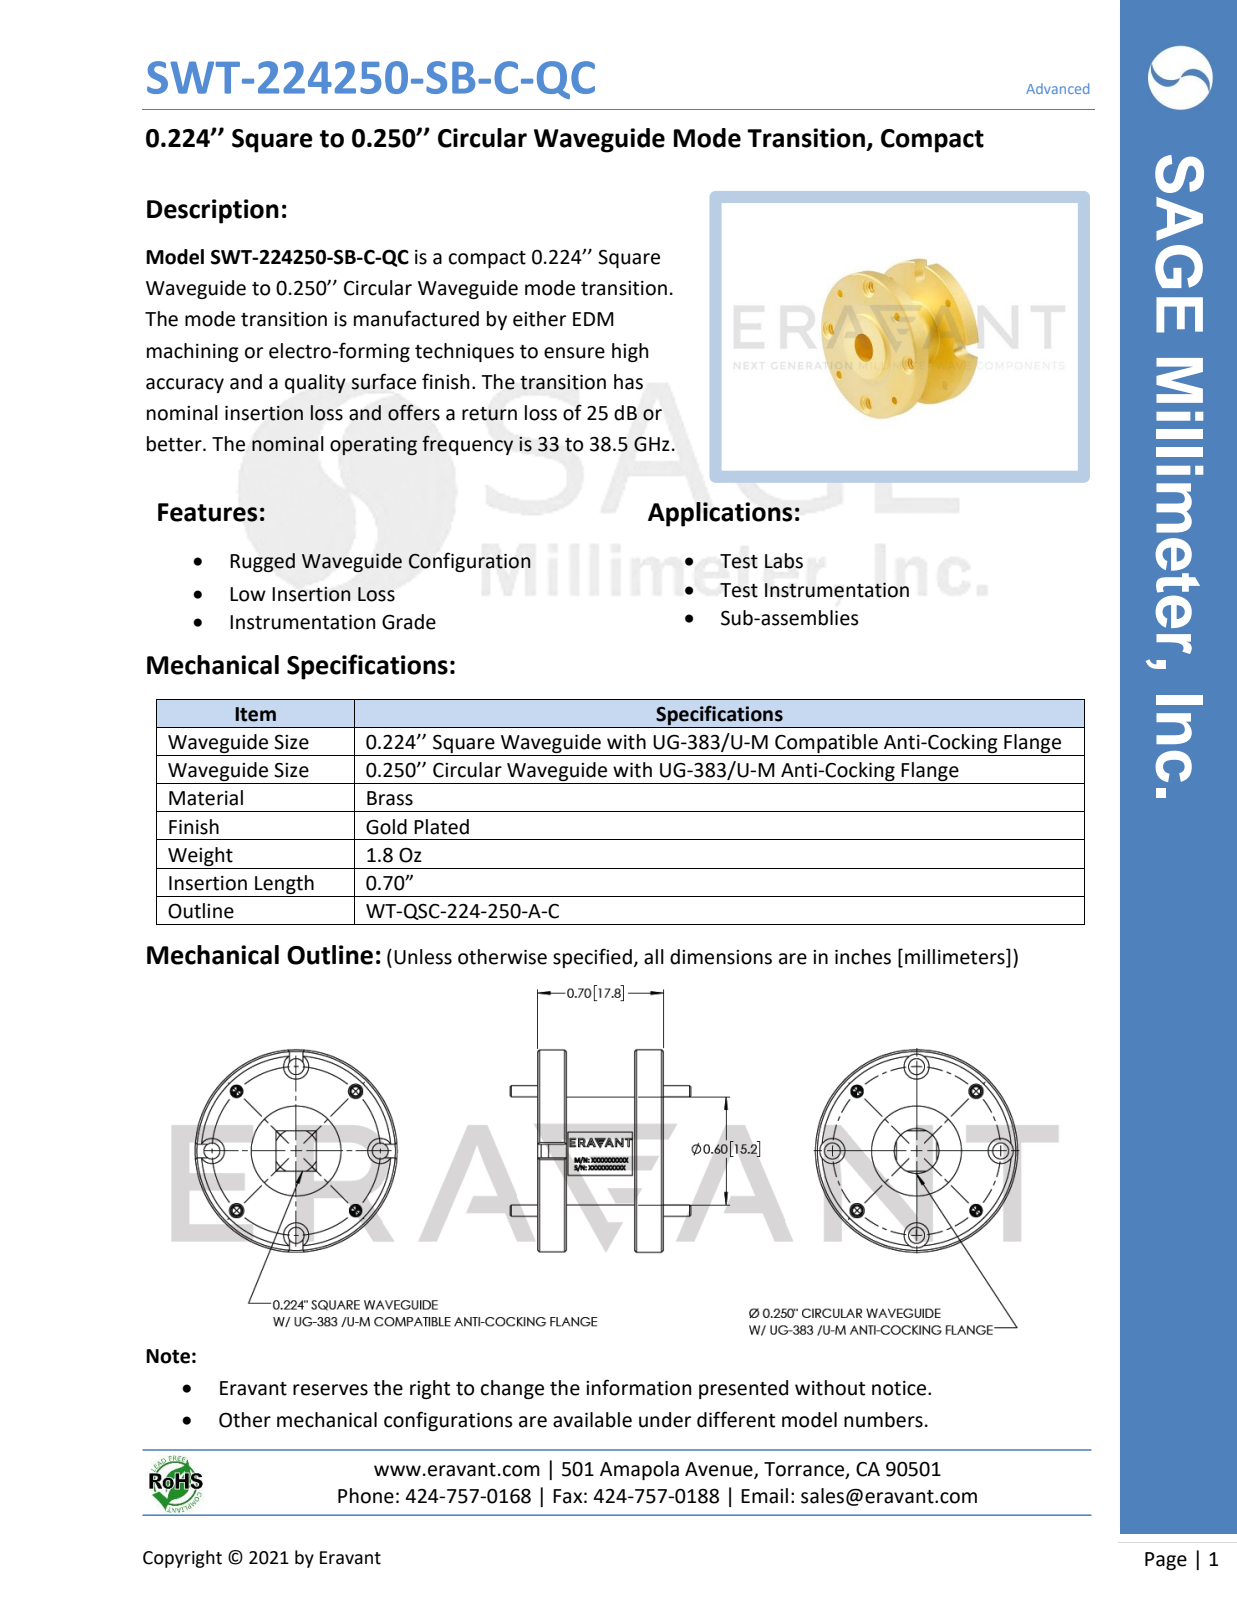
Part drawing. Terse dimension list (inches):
name: WT-QSC-224-250-A-C, Defeatured
written by: SolidWorks 2021 (AUTOMOTIVE_DESIGN)
unit: in
bodies: 5 solids, 178 faces (47 planar, 78 cylindrical, 53 other)
size: 1.125 × 1.125 × 1.005
volume: 0.384 in³; area: 6.006 in²
holes: 4× ⌀0.061, 4× ⌀0.067, 4× ⌀0.089, 4× ⌀0.14, 1× ⌀1.055
bosses: 4× ⌀0.063, 1× ⌀1.125, 1× ⌀1.125, 1× ⌀0.6, 1× ⌀0.5
face distances: 0.14, 0.52, 0.38, 0.66, 0.02, 0.16, 0.54, 0.68, 0.7, 0.69
hole spacings: 0.359, 0.469, 0.663, 0.866, 0.938
